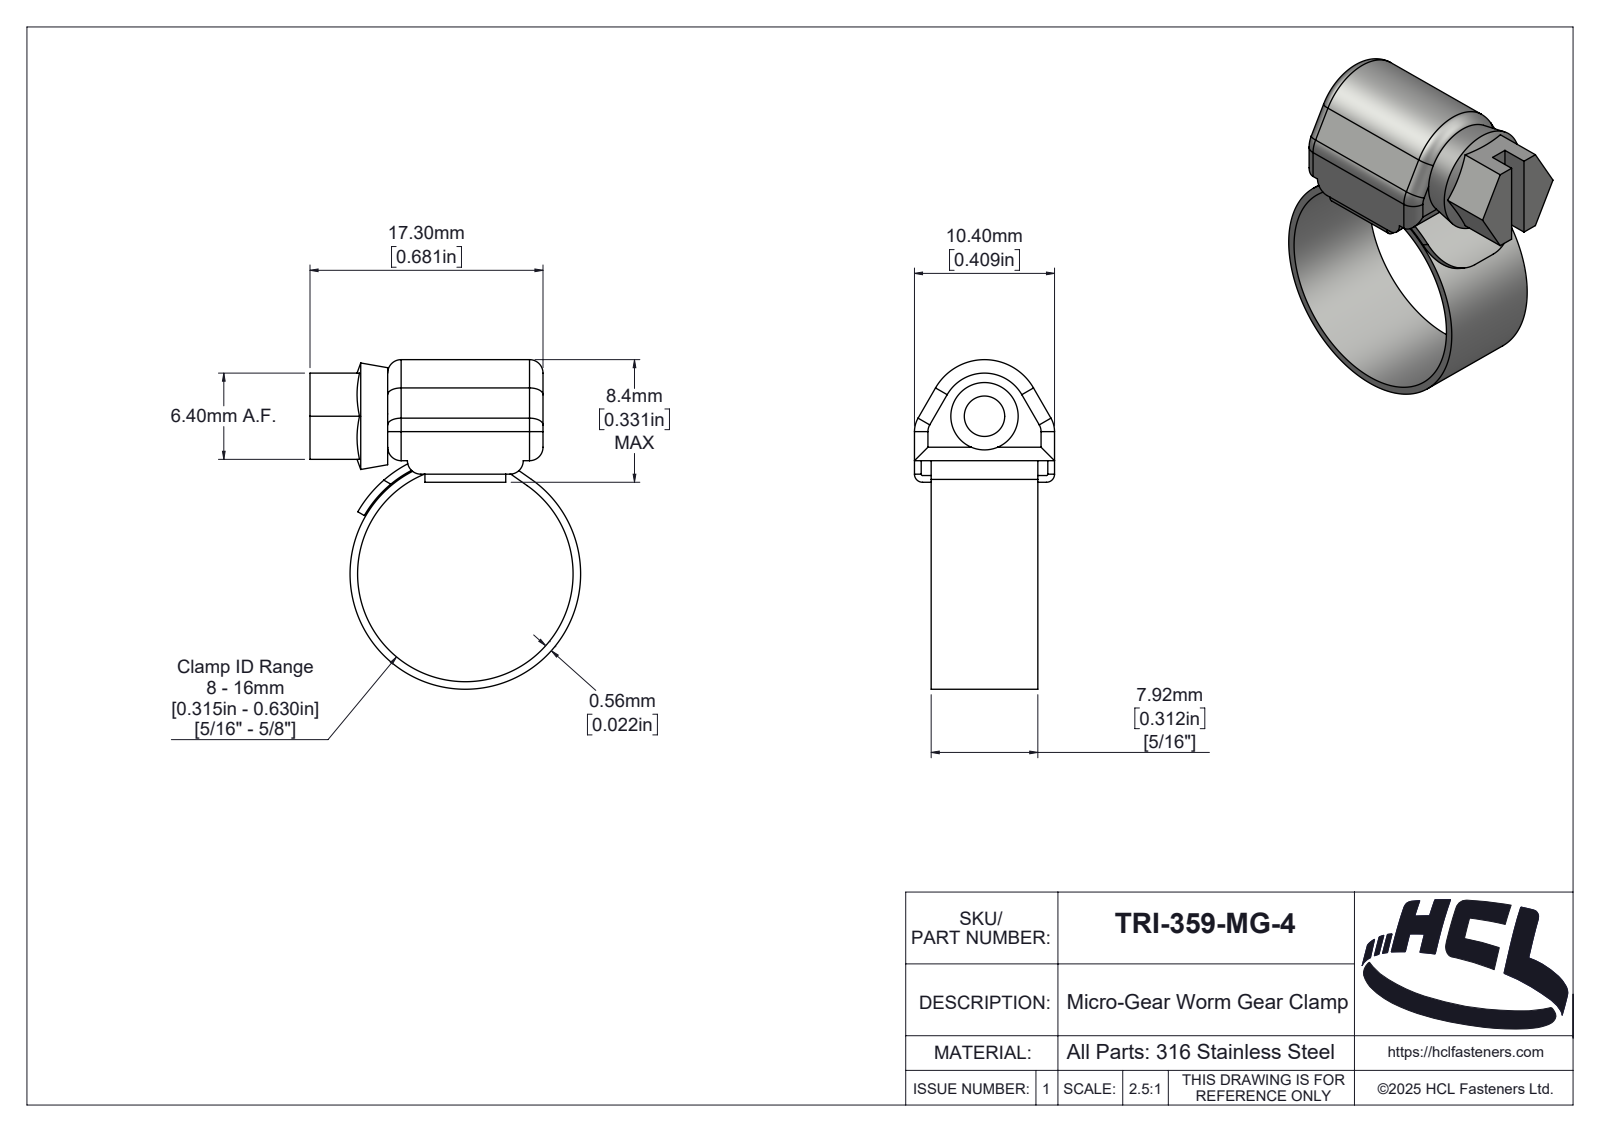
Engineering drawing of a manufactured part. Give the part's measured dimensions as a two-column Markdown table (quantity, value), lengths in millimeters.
| quantity | value |
| --- | --- |
| part name | TRI-359-MG-4 |
| STEP written by | SolidWorks 2025 (AUTOMOTIVE_DESIGN) |
| units | millimeters |
| bodies | 3 solids, 186 faces (38 planar, 87 cylindrical, 61 other) |
| overall size | 24.46 × 20.09 × 10.4 |
| volume | 1 215 mm³ |
| surface area | 2 212 mm² |
| round holes (diameter × count) | 5 × 1, 16 × 1 |
| round bosses / shafts (diameter × count) | 17.12 × 1 |
| partial cylindrical surfaces (radius × count) | 1 × 12, 2 × 3, 0.1 × 2, 0.6 × 2, 3 × 2, 0.25 × 1, 1.01 × 1, 1.26 × 1 |
| main face-to-face distances | 1.1, 0.5, 1.24, 9.16, 1.6, 6.2, 7.92, 10.4, 5.76, 7.3 |
